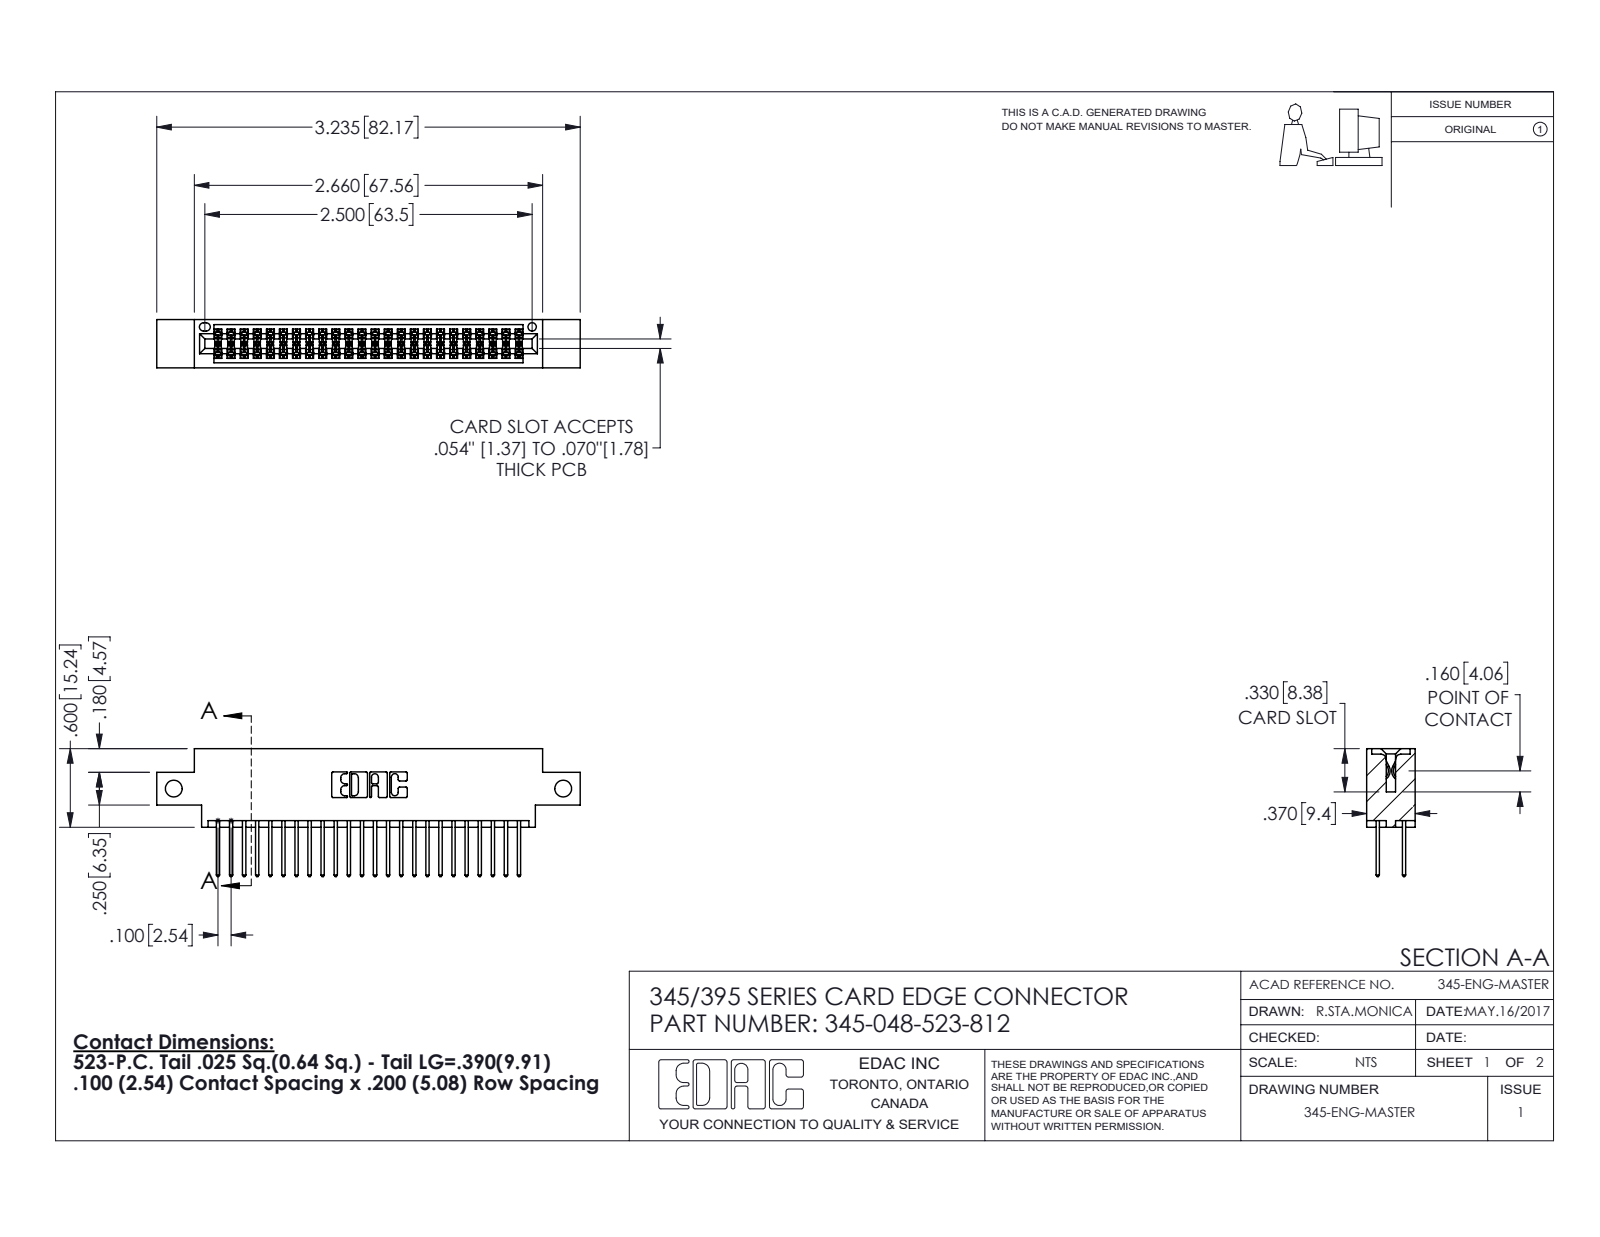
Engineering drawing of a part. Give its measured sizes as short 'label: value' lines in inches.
name: 345-292-001_345-293-123; 345 Part_0.170 Offset - Side Mount; 345-048-523-812
written by: SolidWorks 2016 (CONFIG_CONTROL_DESIGN)
unit: in
bodies: 49 solids, 2530 faces (1668 planar, 862 cylindrical, 0 other)
size: 3.235 × 0.977 × 0.37
volume: 0.471 in³; area: 17.83 in²
holes: 2× ⌀0.128, 1× ⌀0.064
rounds: 72× R0.006, 48× R0.01, 22× R0.01, 6× R0.007, 6× R0.031, 3× R0.026, 2× R0.014, 2× R0.019
face distances: 0.298, 0.072, 0.2, 0.37, 0.098, 0.272, 0.025, 0.225, 0.175, 0.15
hole spacings: 2.975
